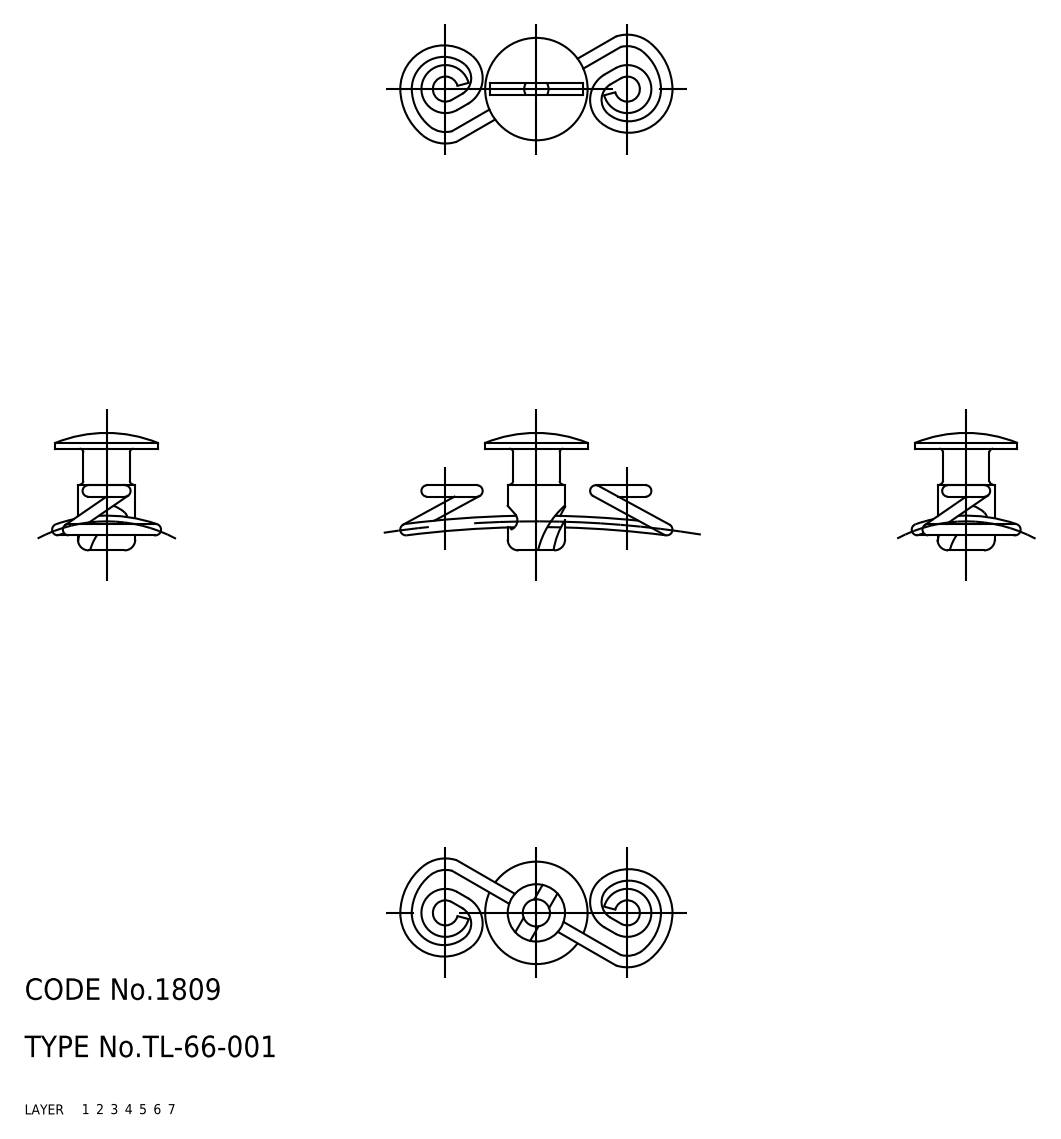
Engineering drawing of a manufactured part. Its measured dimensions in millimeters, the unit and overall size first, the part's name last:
Units: millimetres
Overall size (bounding box): 38.01 × 16.38 × 15.07
Round holes (diameter × count): ⌀3.8 ×1
Round bosses / shafts (diameter × count): ⌀1.6 ×2, ⌀14.3 ×1, ⌀8 ×1, ⌀6.5 ×1
Partial cylindrical surfaces — rounded edges, fillets, slot ends (radius × count): R1.2 ×2, R2.94 ×2, R5.34 ×2
Main face-to-face distances: 1.05, 1.7, 5, 6.05, 9.2, 14.2, 15.25, 6.58
Volume: 822 mm³ · Surface area: 1 467 mm²
Bodies: 2 solids, 77 faces (14 planar, 24 cylindrical, 39 other)
Part name (STEP PRODUCT): spring; TL_66_001; fastener
STEP written by: SolidWorks 2015 (AUTOMOTIVE_DESIGN)
